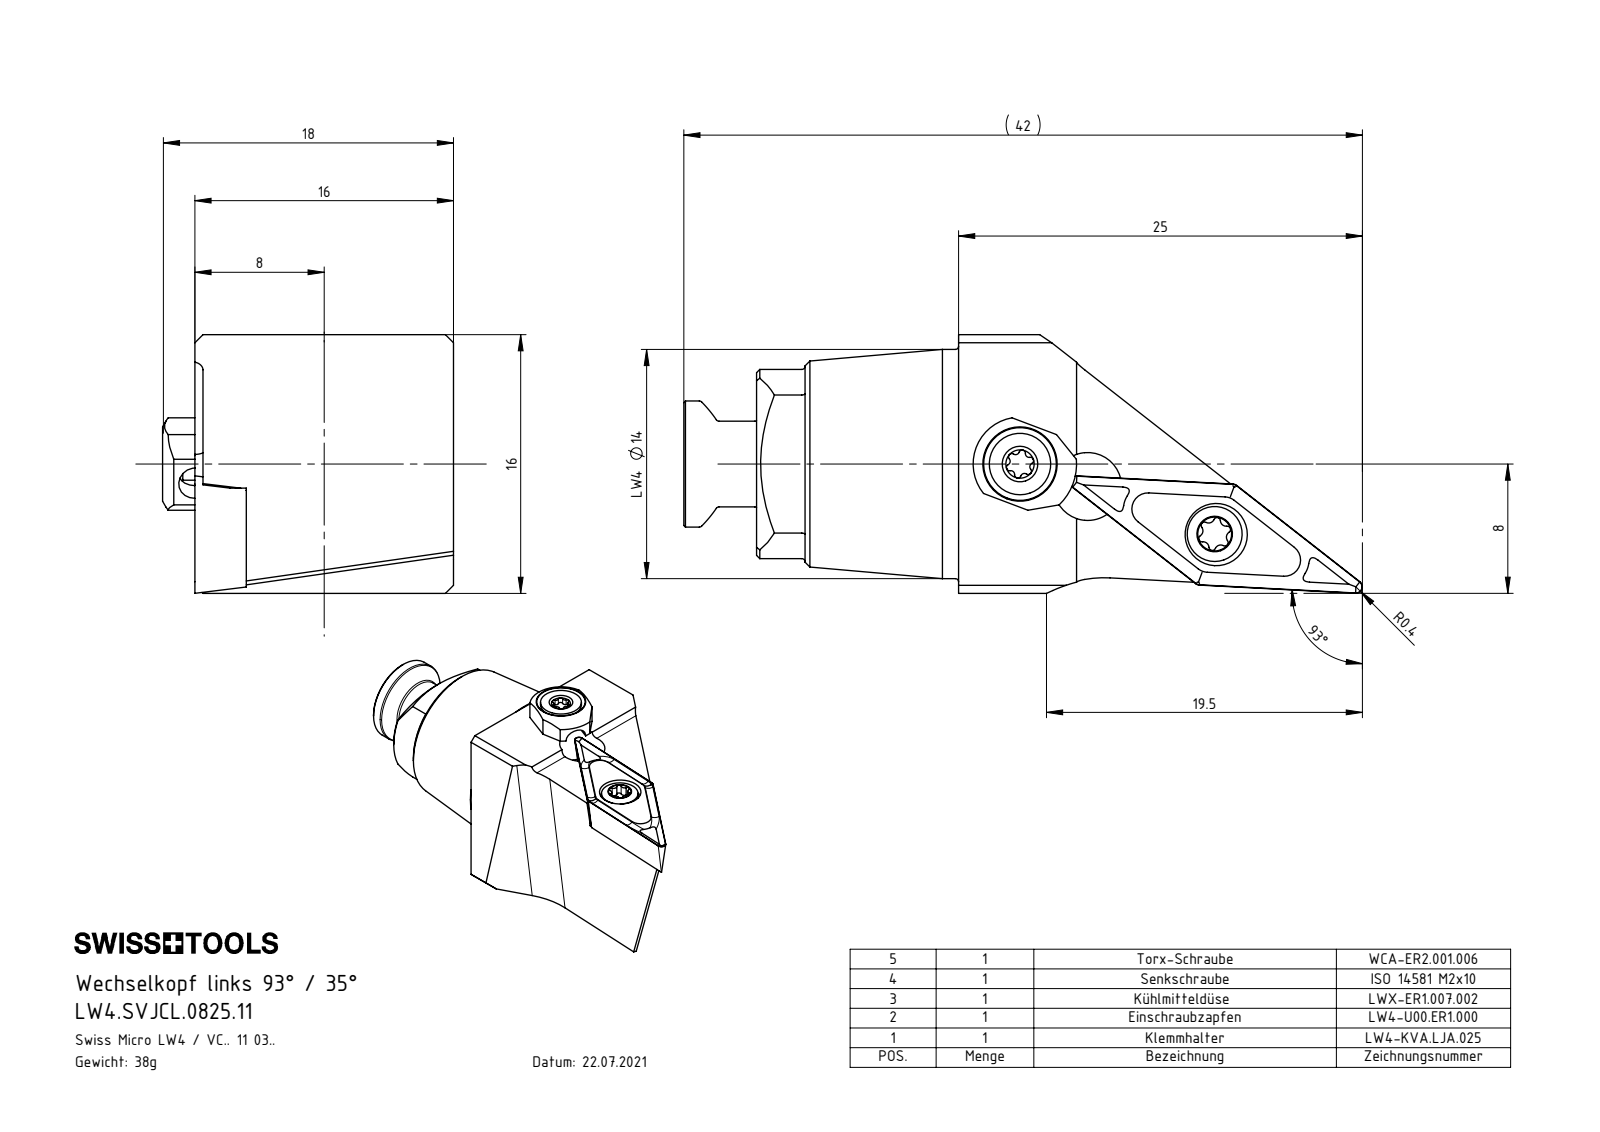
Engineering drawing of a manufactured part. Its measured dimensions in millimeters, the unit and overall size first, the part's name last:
Units: millimetres
Overall size (bounding box): 41.98 × 18 × 16
Round holes (diameter × count): ⌀2 ×2, ⌀1.6 ×1, ⌀2.05 ×1, ⌀2.5 ×1, ⌀2.8 ×1, ⌀3 ×1, ⌀3.85 ×1, ⌀4.2 ×1, ⌀5.5 ×1
Round bosses / shafts (diameter × count): ⌀14.17 ×1, ⌀7.7 ×1, ⌀6 ×1, ⌀5.3 ×1, ⌀5 ×1, ⌀3.8 ×1, ⌀3.4 ×1, ⌀2.5 ×1
Partial cylindrical surfaces — rounded edges, fillets, slot ends (radius × count): R0.2 ×8, R0.21 ×6, R0.24 ×6, R0.36 ×4, R0.36 ×2, R0.5 ×1, R1 ×1, R2.9 ×1
Main face-to-face distances: 16, 12.82, 3.18, 7.5, 15.5, 2.68, 0.5, 2, 12.5, 4
Hole centre spacings: 4.41, 8.39, 8.49, 12.8, 12.9
Volume: 4 681 mm³ · Surface area: 3 201 mm²
Bodies: 6 solids, 261 faces (70 planar, 82 cylindrical, 109 other)
Part name (STEP PRODUCT): ISO 14581 - M2x10; LWX-ER1.007.002; VCGT110304; LW4.SVJCL.0825.11 (+3 more)
STEP written by: SolidWorks 2022 (CONFIG_CONTROL_DESIGN)
